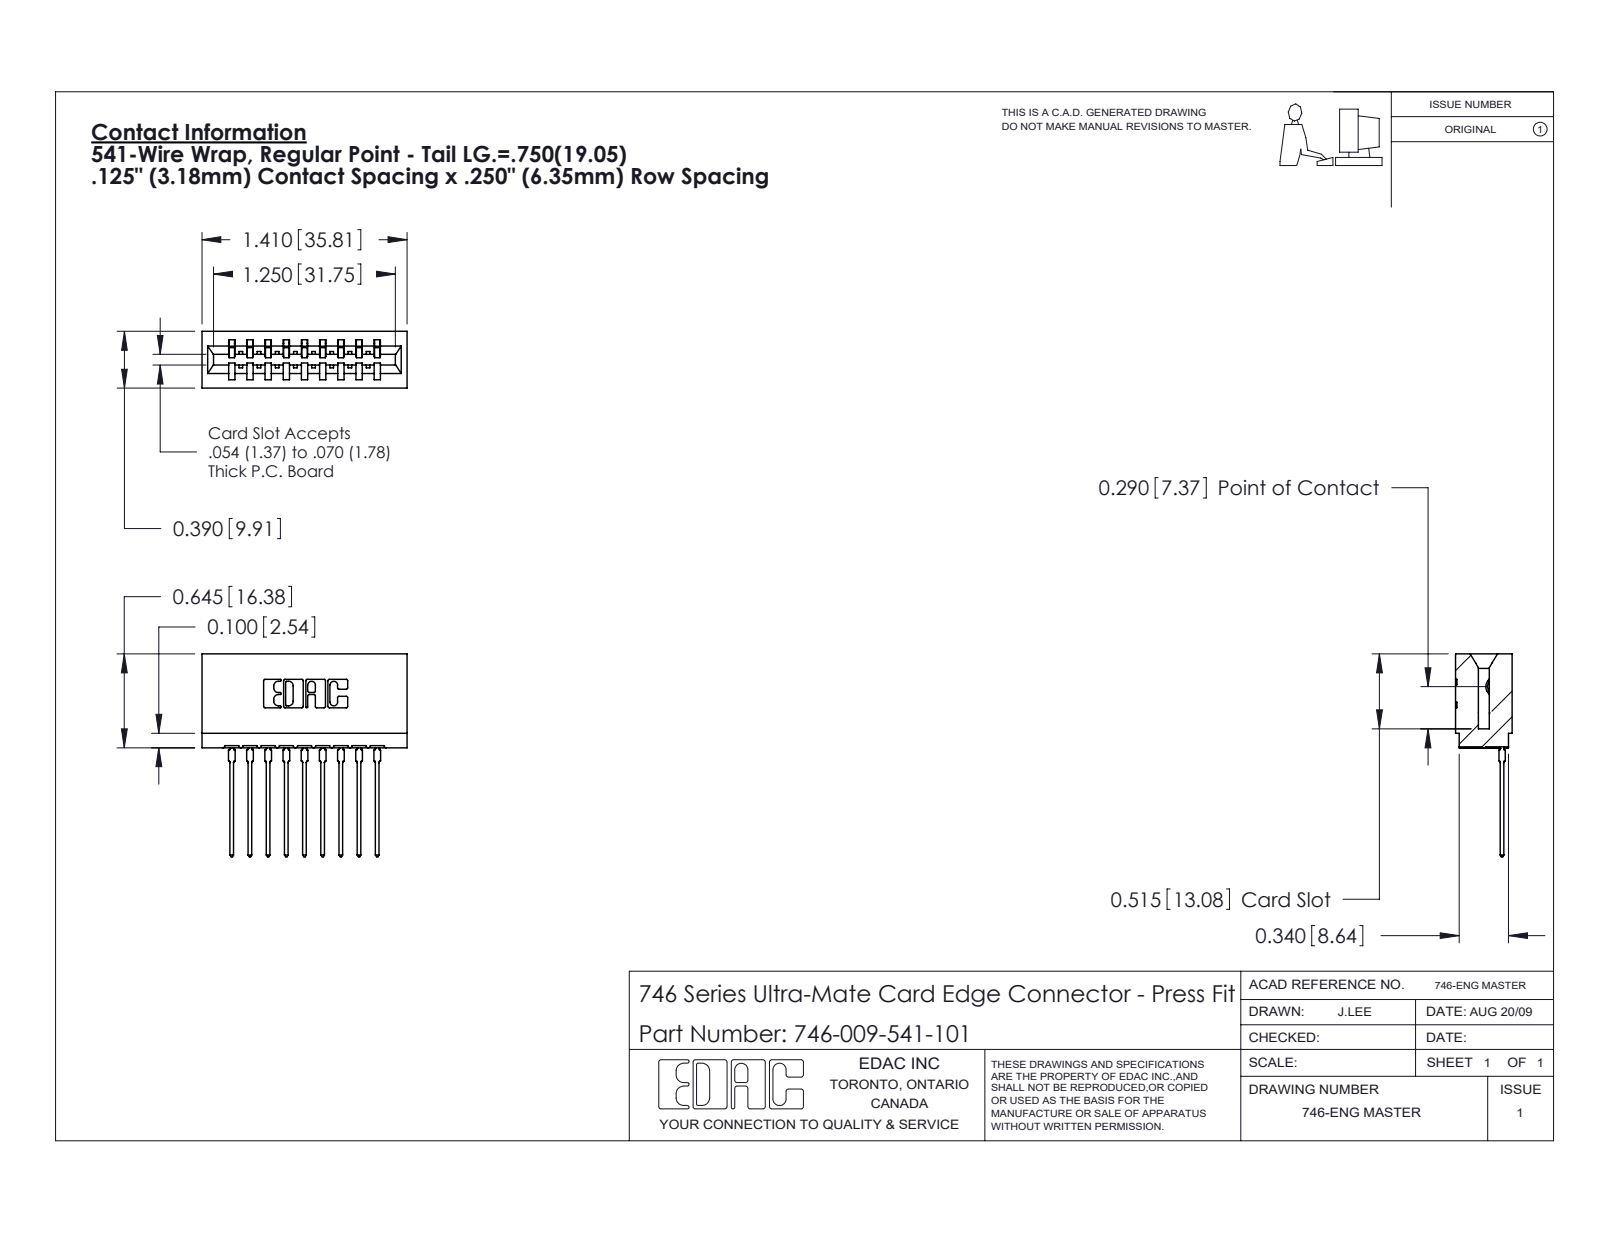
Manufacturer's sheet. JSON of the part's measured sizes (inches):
{"part_name": "746 Part_.515 Slot Depth - 01; 746-009-541-101; 746-292-001_541", "step_written_by": "SolidWorks 2020 (CONFIG_CONTROL_DESIGN)", "units": "inches", "bodies": {"solids": 10, "faces": 1069, "planar": 622, "cylindrical": 213, "other": 234}, "overall_size": [1.41, 1.394, 0.39], "volume_in3": 0.245, "surface_area_in2": 8.689, "partial_cylinders_radius": [[0.01, 22], [0.021, 18], [0.015, 10], [0.007, 6], [0.031, 6], [0.005, 4], [0.011, 4], [0.026, 3]], "face_to_face_distances": [0.25, 0.5, 0.333, 0.042, 0.125, 0.125, 0.057, 0.292, 0.208, 0.083]}
